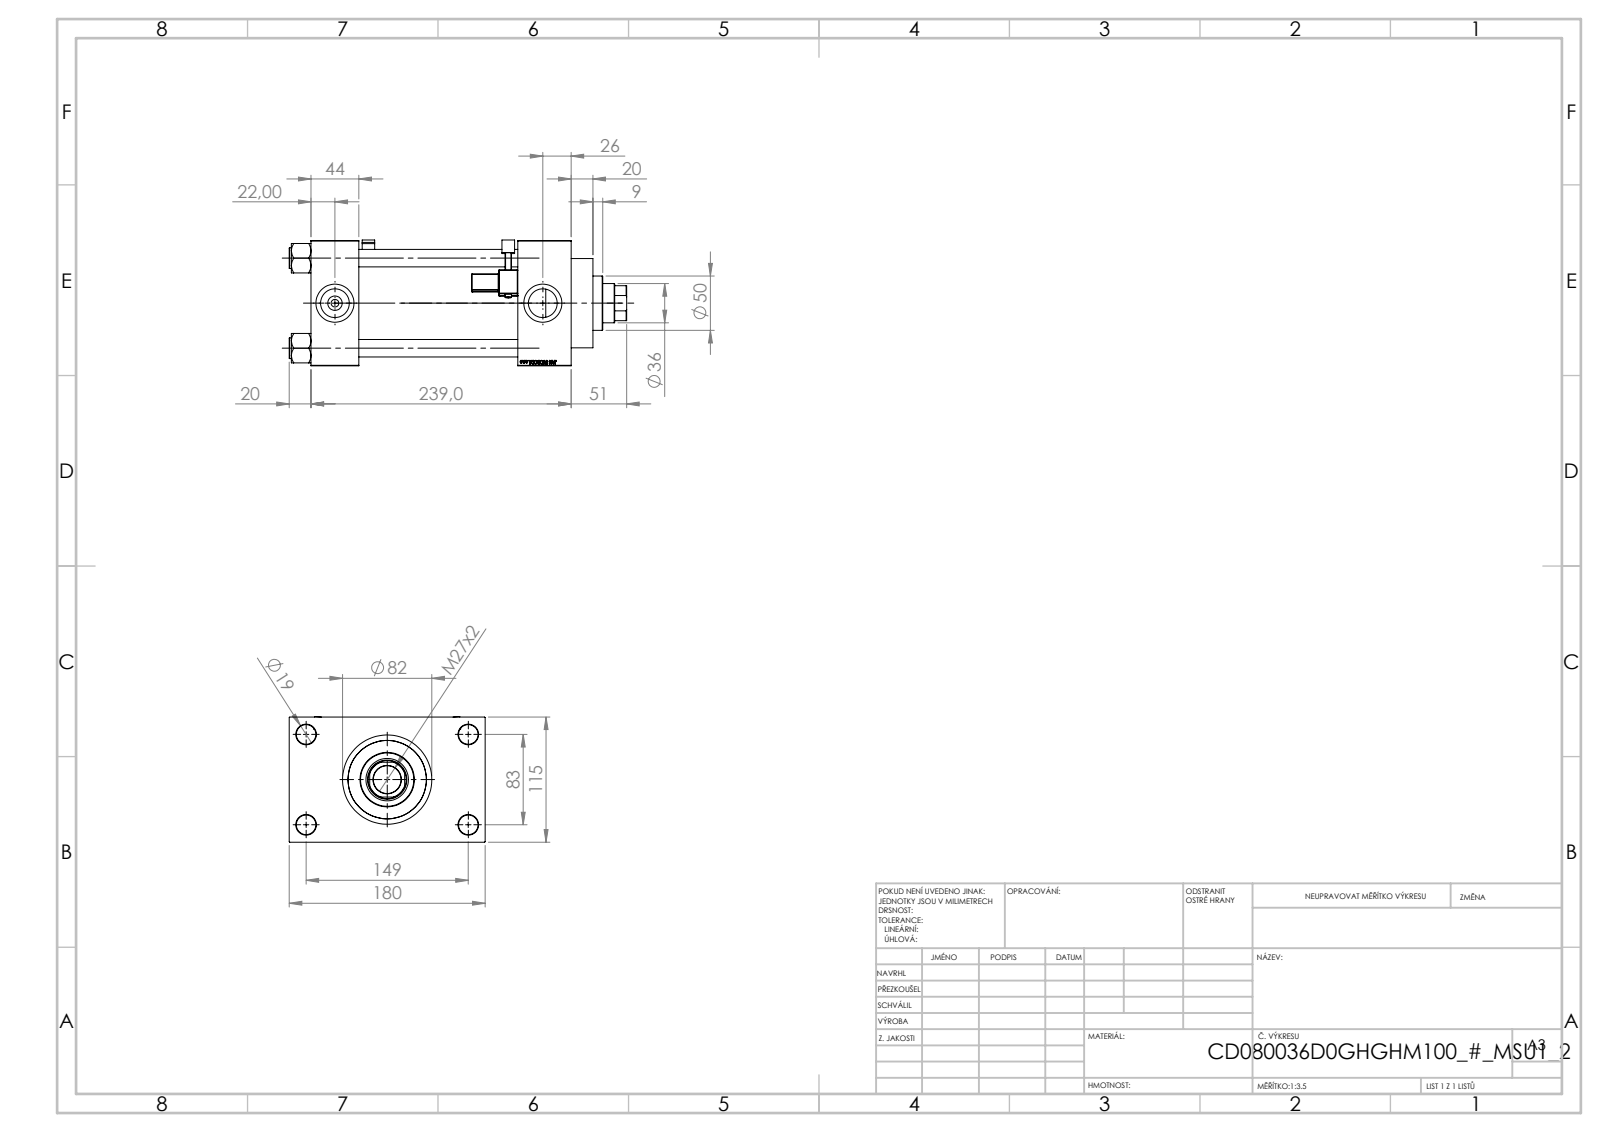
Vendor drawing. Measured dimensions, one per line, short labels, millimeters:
name: V215CD_VC_A; V215CR_MSU; V215CD_VCP_D; V215CD_D_Body (+2 more)
written by: SolidWorks 2019 (CONFIG_CONTROL_DESIGN)
unit: mm
bodies: 13 solids, 1305 faces (603 planar, 148 cylindrical, 554 other)
size: 310 × 180 × 115.49
volume: 2 229 000 mm³; area: 375 899 mm²
holes: 4× ⌀16, 4× ⌀18, 2× ⌀7, 2× ⌀26.44, 2× ⌀35, 1× ⌀25.5, 1× ⌀36, 1× ⌀39, 1× ⌀61, 1× ⌀72, 1× ⌀80
bosses: 4× ⌀19, 2× ⌀6, 1× ⌀86, 1× ⌀82, 1× ⌀50
rounds: 48× R0.5, 2× R1, 2× R2.5, 2× R4, 1× R17.5
face distances: 115, 146, 195, 49, 44, 190, 239, 32.5, 147.5, 20
hole spacings: 33.15, 58.48, 82.7, 85.28, 89.24, 115.85, 142.43, 83
